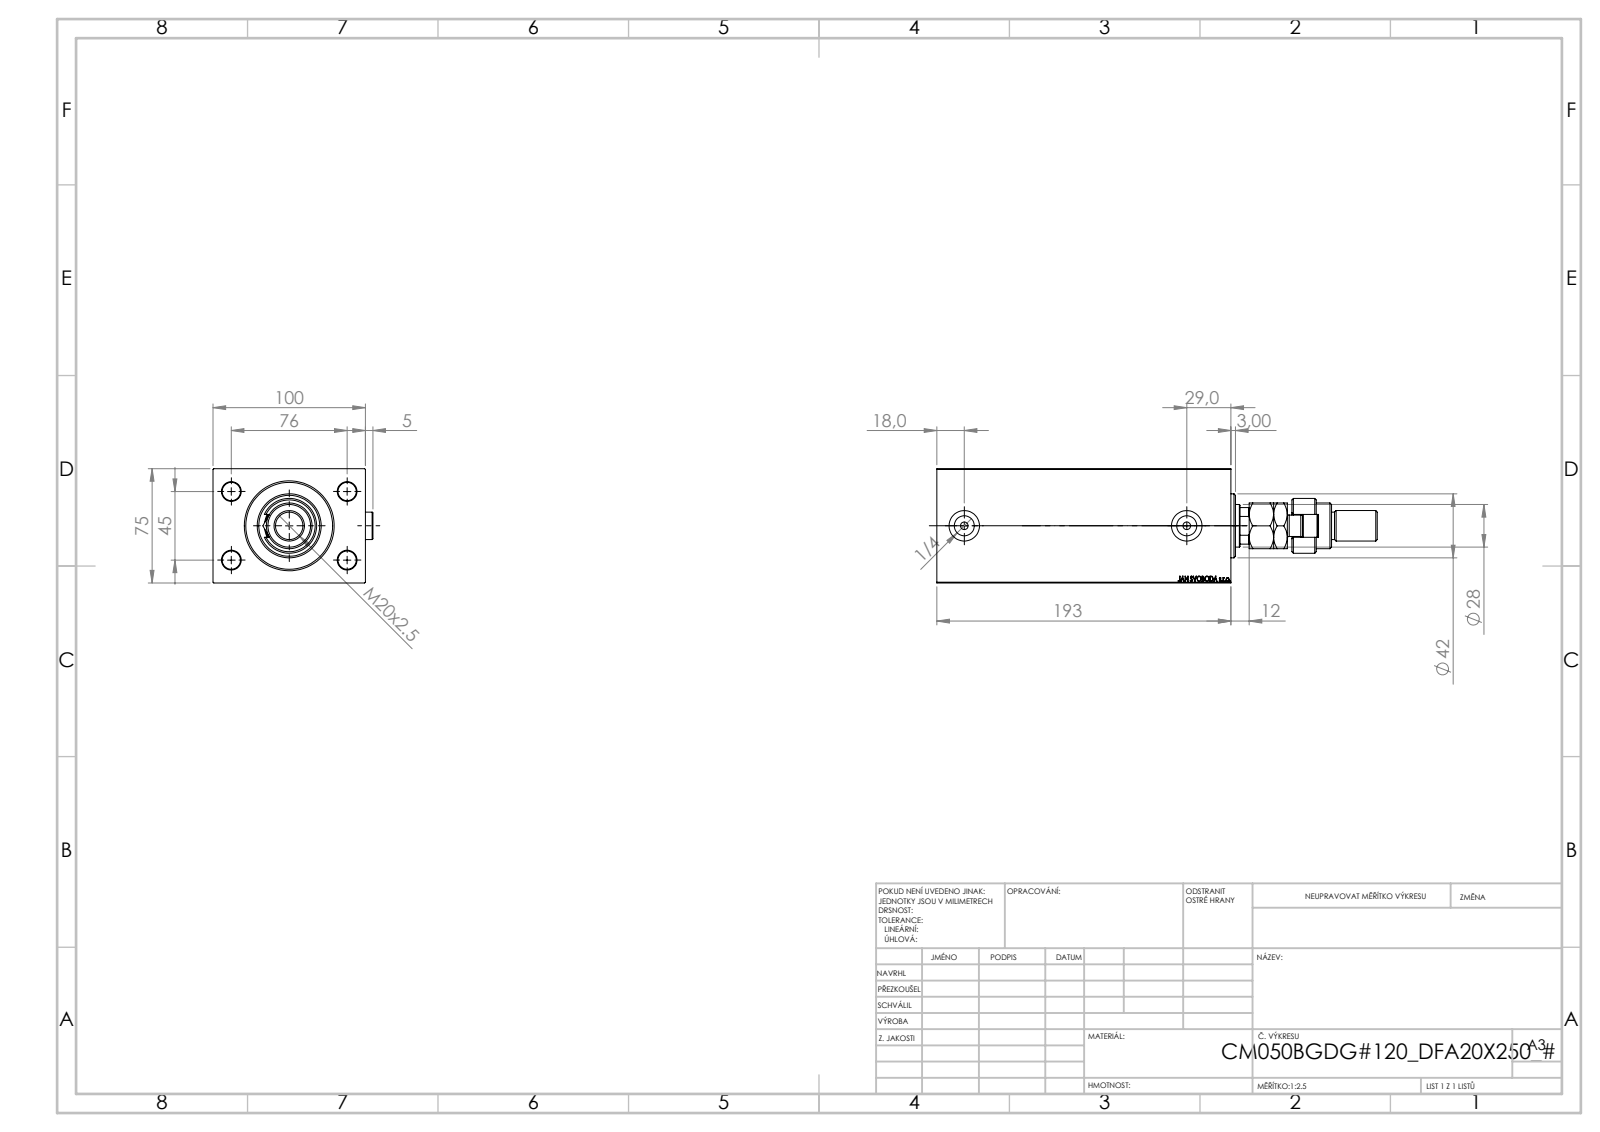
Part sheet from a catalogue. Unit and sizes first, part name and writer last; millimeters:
Units: millimetres
Overall size (bounding box): 289 × 104.9 × 75
Round holes (diameter × count): ⌀12 ×4, ⌀5 ×2, ⌀13.16 ×2, ⌀20 ×2, ⌀18.5 ×1, ⌀28 ×1, ⌀31.5 ×1, ⌀32.5 ×1, ⌀50 ×1, ⌀52 ×1, ⌀57 ×1
Round bosses / shafts (diameter × count): ⌀18 ×3, ⌀42 ×1, ⌀36 ×1, ⌀30 ×1, ⌀22 ×1, ⌀20 ×1, ⌀14 ×1
Partial cylindrical surfaces — rounded edges, fillets, slot ends (radius × count): R7.5 ×1, R12 ×1, R13.5 ×1
Main face-to-face distances: 75, 100, 193, 179, 14, 12, 30, 181, 167, 47
Hole centre spacings: 44.16, 45, 76, 88.32, 146
Volume: 1 311 000 mm³ · Surface area: 167 384 mm²
Bodies: 7 solids, 1023 faces (464 planar, 85 cylindrical, 474 other)
Part name (STEP PRODUCT): V450CM_B_Body; FEMALE_PART_FOR_DFA; V450CM_B_VCP; Zatka_OIL_PORT (+2 more)
STEP written by: SolidWorks 2019 (CONFIG_CONTROL_DESIGN)
